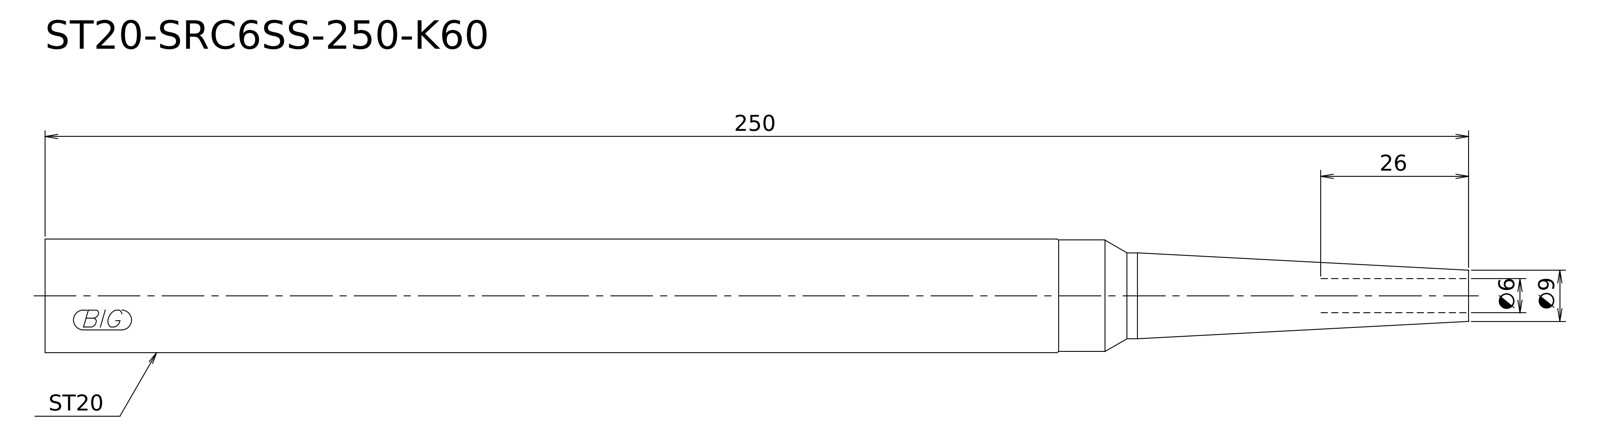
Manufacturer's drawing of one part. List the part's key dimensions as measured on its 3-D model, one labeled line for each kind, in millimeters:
STEP written by: Kubotek KeyCreator V8.5.1 (14335) (CONFIG_CONTROL_DESIGN)
Units: millimetres
Bodies: 1 solid, 8 faces (2 planar, 3 cylindrical, 3 other)
Overall size (bounding box): 250 × 20 × 20
Volume: 66 391 mm³ · Surface area: 14 601 mm²
Round bosses / shafts (diameter × count): ⌀20 ×1, ⌀19.6 ×1, ⌀15.1 ×1
Main face-to-face distances: 250
